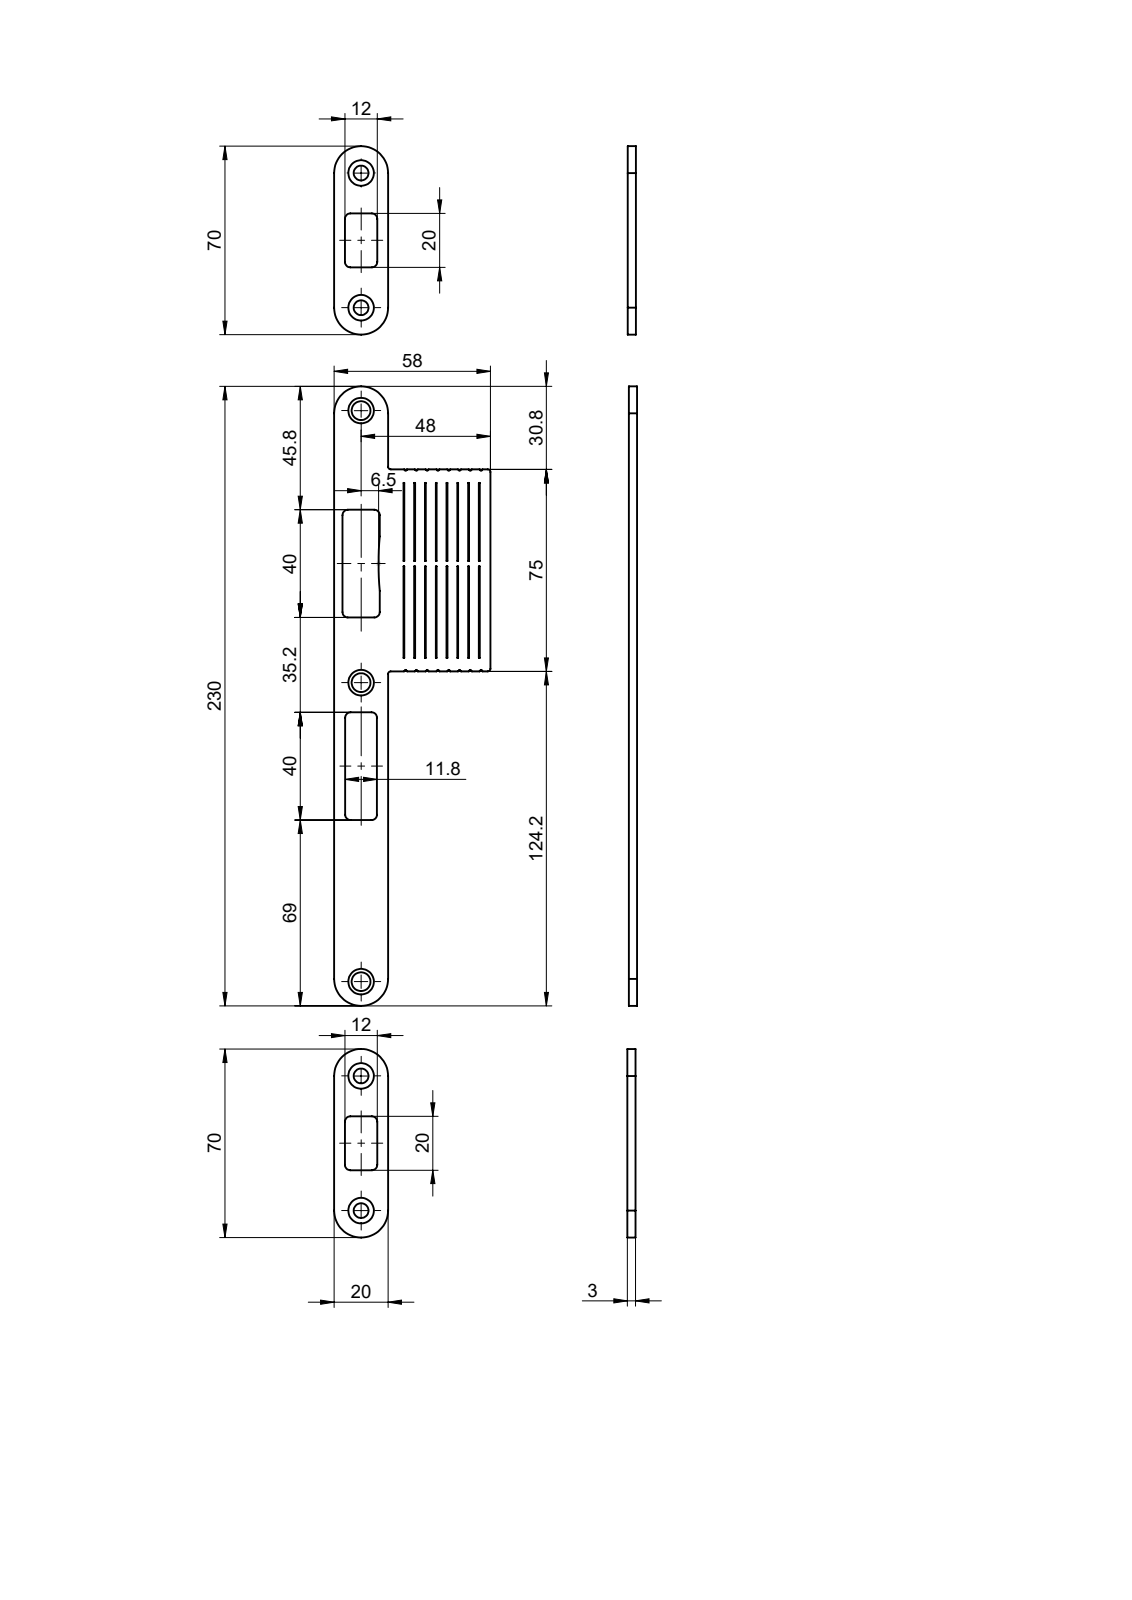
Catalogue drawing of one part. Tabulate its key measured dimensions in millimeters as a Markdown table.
| quantity | value |
| --- | --- |
| part name | D001106194-000_D001106194-001; D001106228-000_D001106228-001; D001106234-000 |
| STEP written by | SolidWorks 2021 (AUTOMOTIVE_DESIGN) |
| units | millimeters |
| bodies | 3 solids, 236 faces (113 planar, 103 cylindrical, 20 other) |
| overall size | 405.2 × 58 × 3.56 |
| volume | 24 135 mm³ |
| surface area | 23 246 mm² |
| round holes (diameter × count) | 5.5 × 4, 7 × 3 |
| partial cylindrical surfaces (radius × count) | 0.3 × 48, 2 × 16, 10 × 6, 1 × 4, 127 × 1 |
| main face-to-face distances | 3, 4, 8, 0.56, 0.42, 20, 12, 16, 4.3, 3.7 |
| hole center spacings | 50, 335.2, 35, 38.2, 85, 88.2, 101, 111 |
